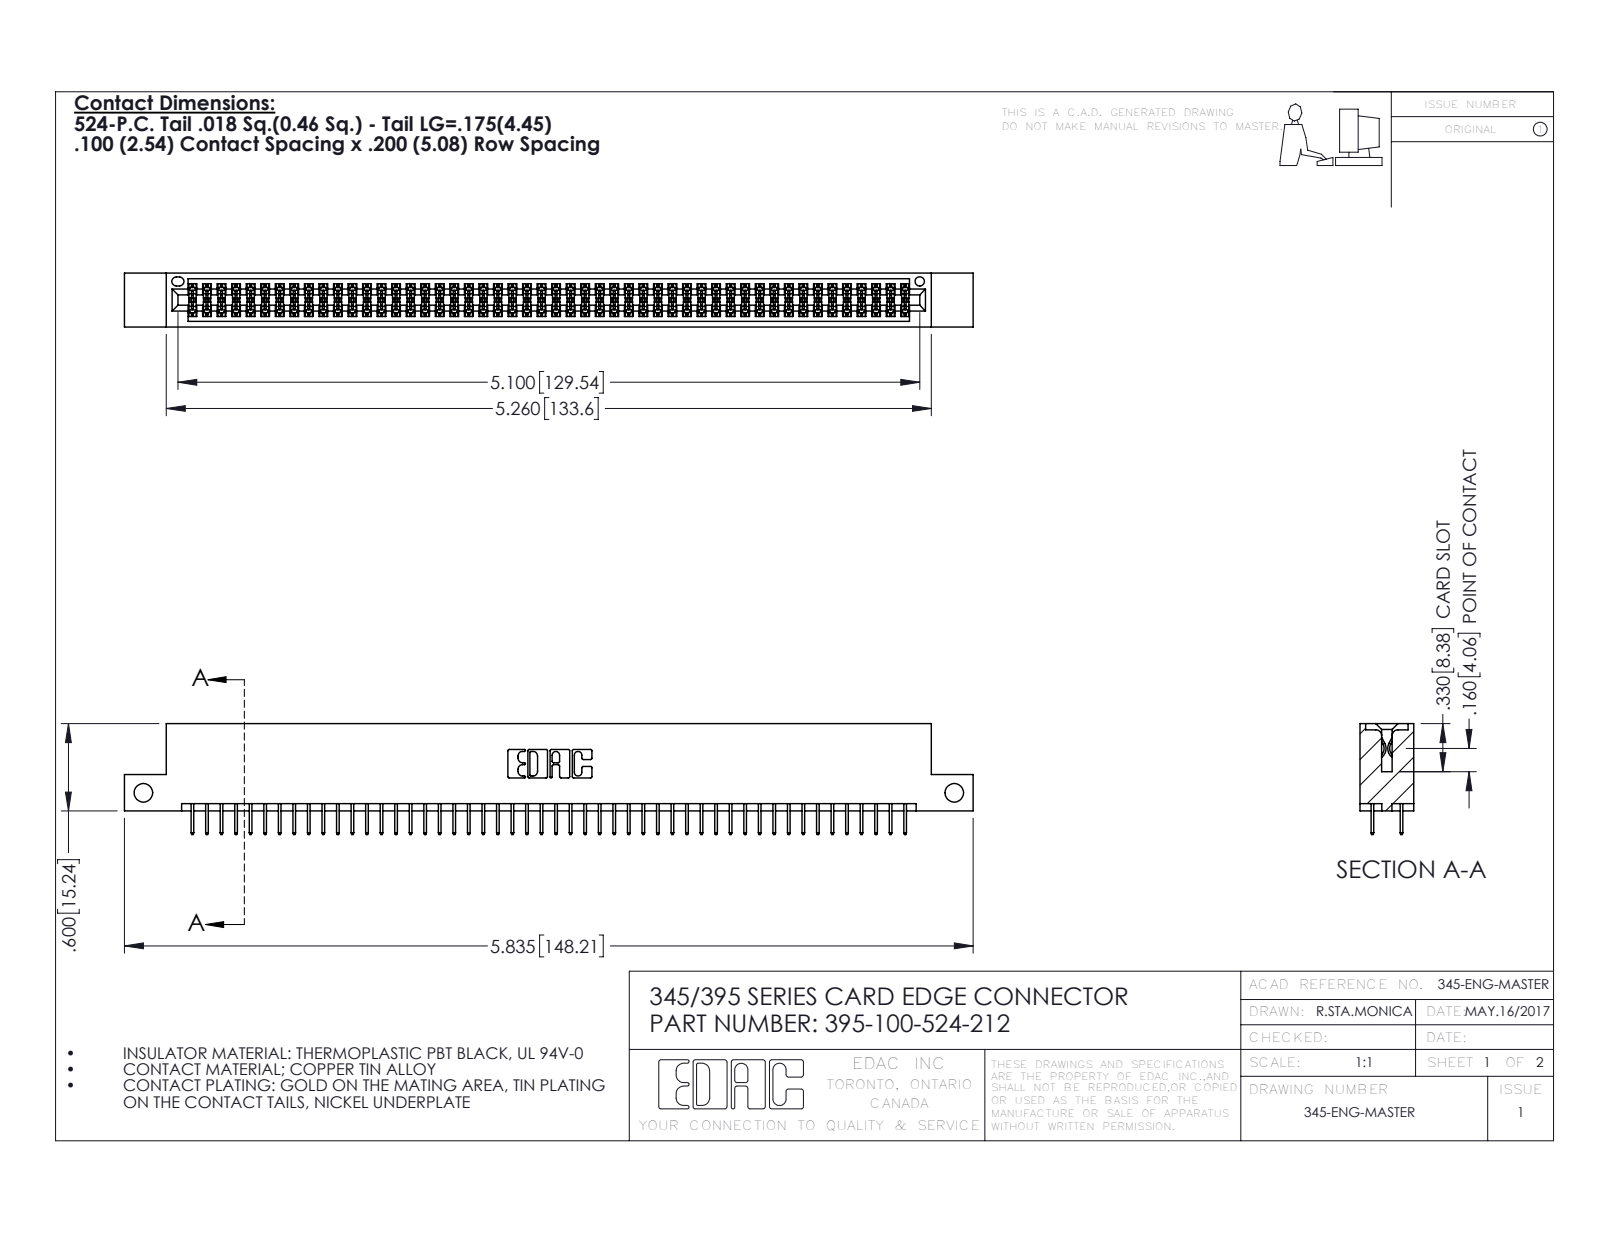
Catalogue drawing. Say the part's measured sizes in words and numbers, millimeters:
The part is named "345 Part_Flush Mounting Lugs - Side Mount; 345-292-001_345-293-124; 395-100-524-212". Its 3-D file was written by "SolidWorks 2016 (CONFIG_CONTROL_DESIGN)". It is 101 solids with 5526 faces: 3980 planar, 1546 cylindrical and 0 other. Overall it measures 148.2 by 19.4 by 9.4 millimeters. Its volume is 14 200 cubic millimeters and its surface area 20 660 square millimeters. Round holes: 2 of diameter 3.3, 1 of diameter 1.6. Partial cylindrical surfaces (rounded edges, fillets, slot ends): 150 of radius 0.2, 22 of radius 0.3, 6 of radius 0.2, 6 of radius 0.8, 3 of radius 0.7, 2 of radius 0.4, 2 of radius 0.5, 2 of radius 0.6. The main face-to-face distances are 7.6, 1.8, 5.1, 9.4, 2.5, 6.9, 0.6, 5.7, 1.8, 4.4. The hole center spacings are 141.6.
